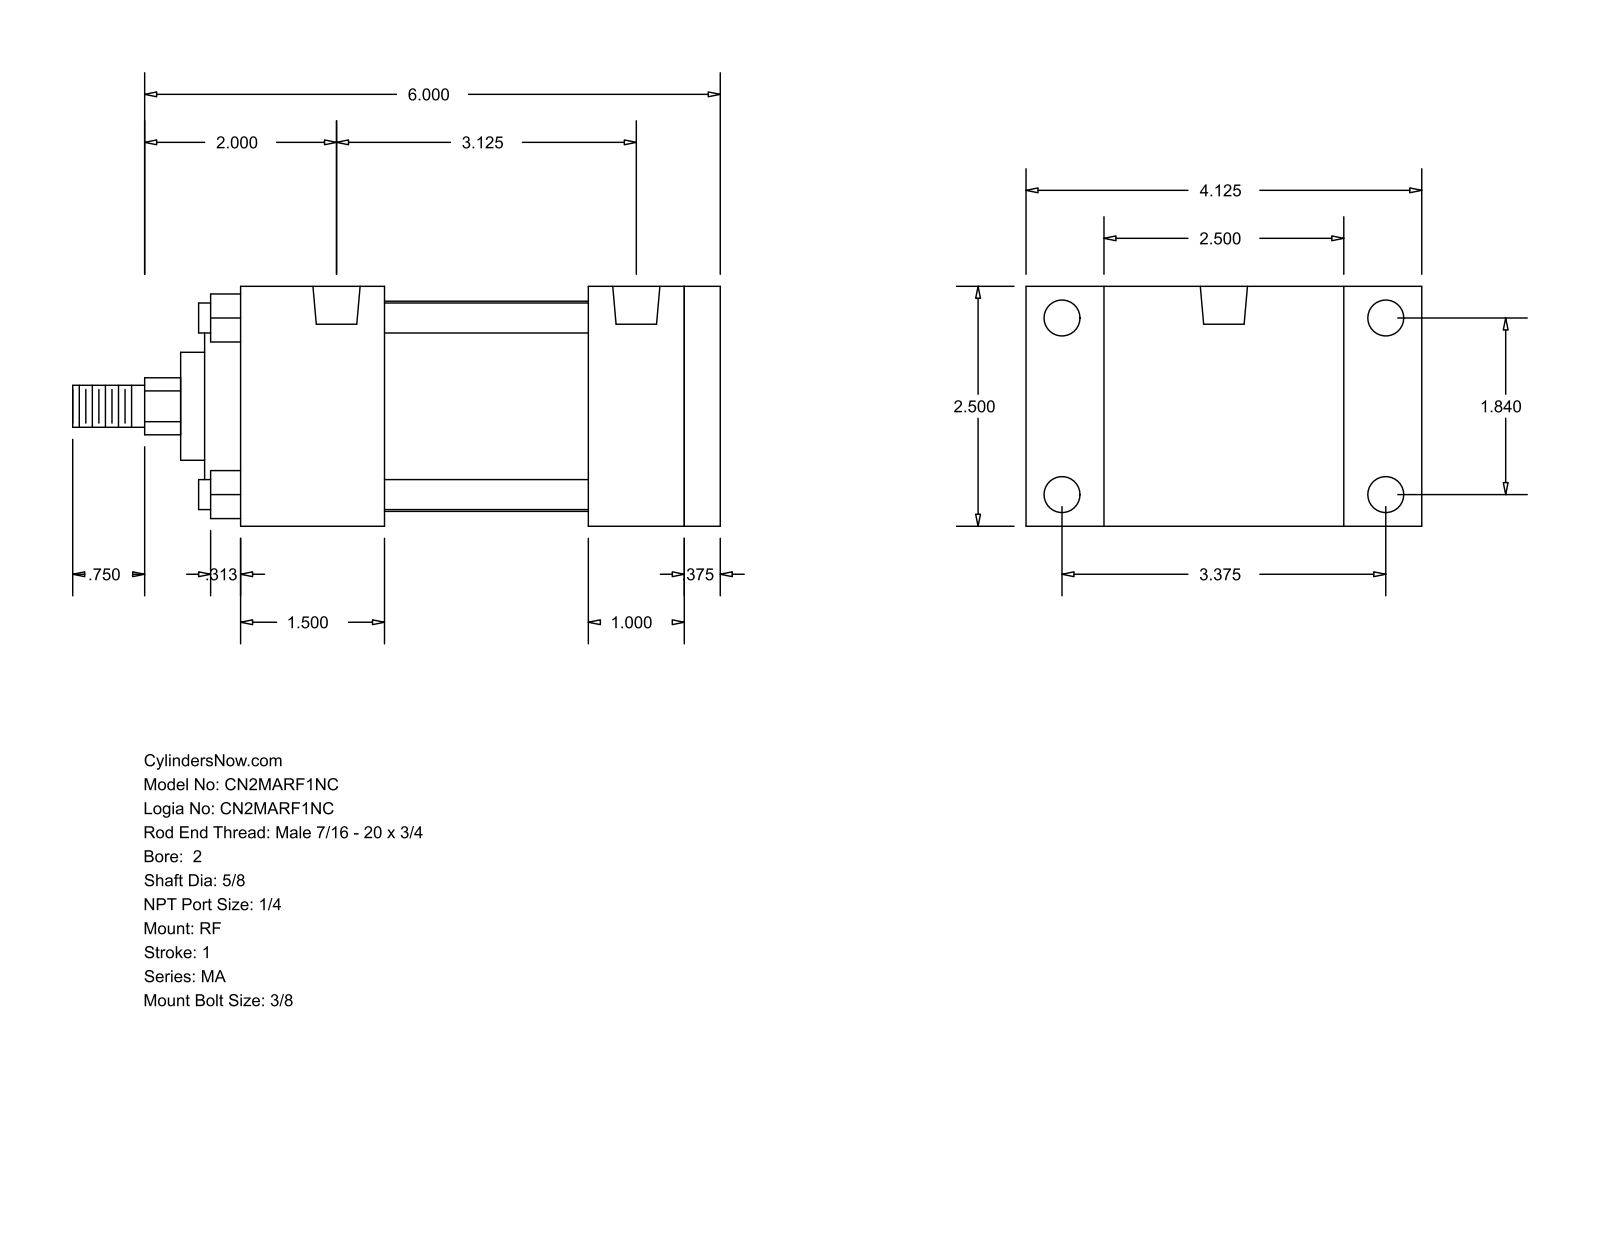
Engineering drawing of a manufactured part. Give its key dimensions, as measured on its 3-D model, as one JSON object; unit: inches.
{"part_name": "MA_RF__0200_0.625", "step_written_by": "GSSL Pune (CONFIG_CONTROL_DESIGN)", "units": "inches", "bodies": {"solids": 0, "faces": 94, "planar": 65, "cylindrical": 29, "other": 0}, "overall_size": [6.75, 4.125, 2.5], "round_holes": [[0.313, 4], [0.375, 4], [0.492, 2]], "round_bosses_or_shafts": [[0.313, 4], [2.19, 1], [2, 1], [1.125, 1], [0.625, 1], [0.437, 1]], "partial_cylinders_radius": [[0.297, 1]], "face_to_face_distances": [2.5, 0.375, 5, 2.125, 1.5, 1.375, 5.375, 4.625, 3.125, 3.5], "hole_center_spacings": [1.84, 3.125, 3.375, 3.844]}
